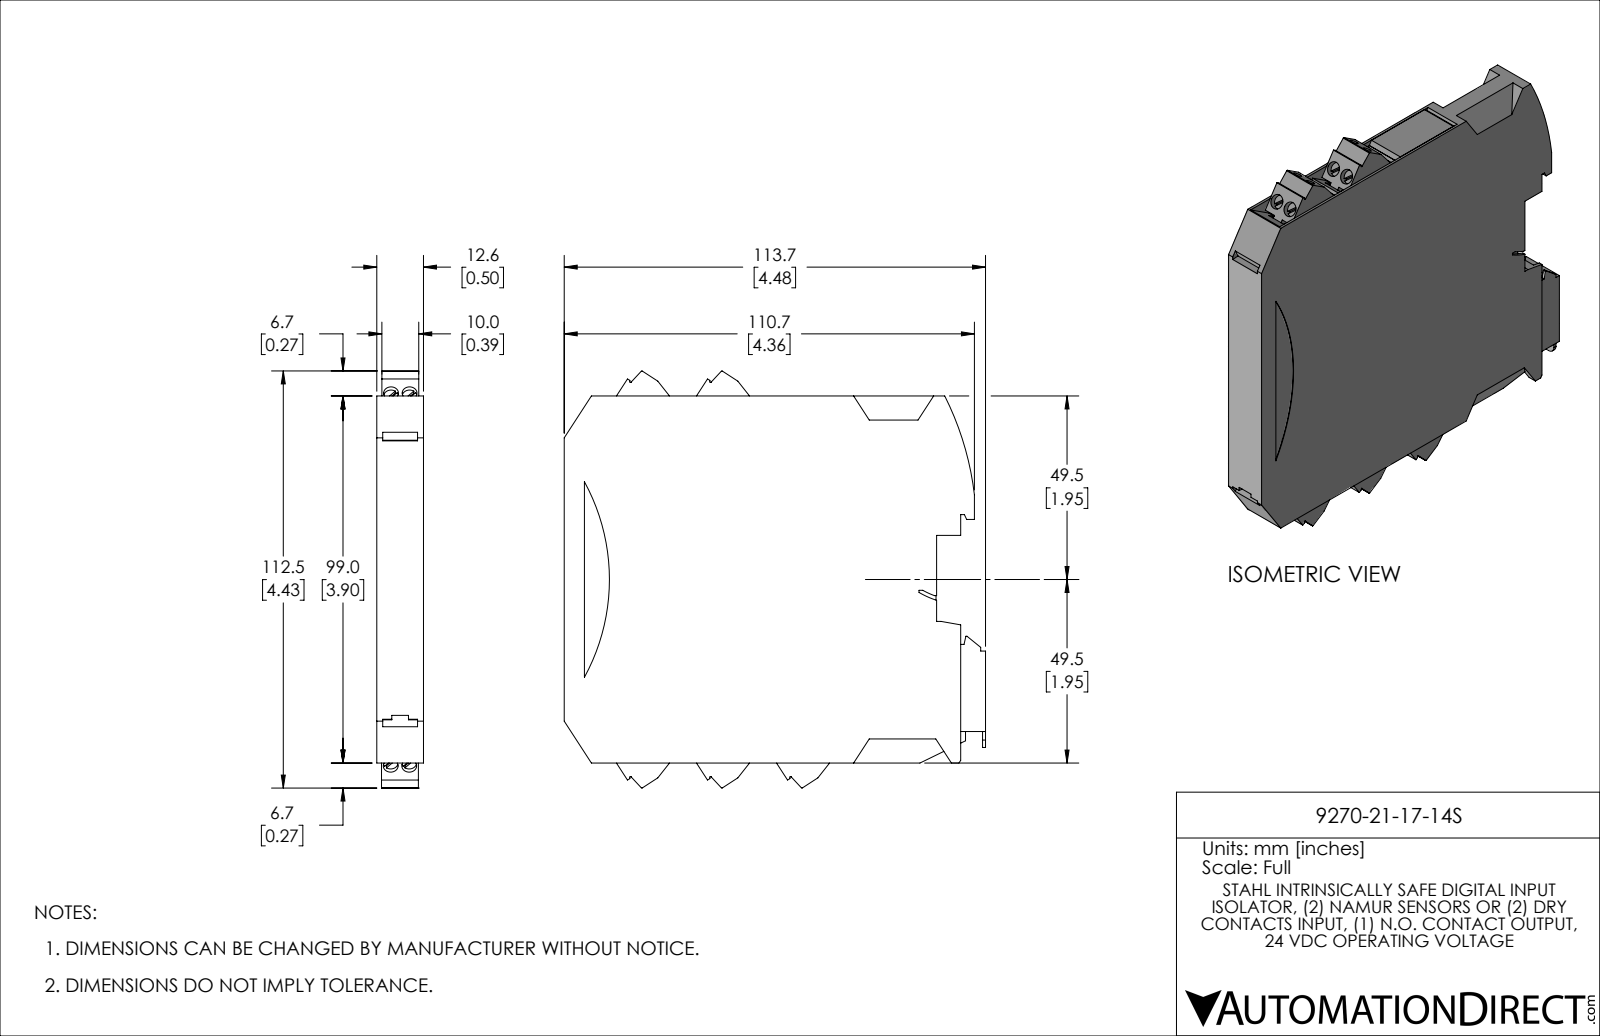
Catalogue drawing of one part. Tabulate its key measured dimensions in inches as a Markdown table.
| quantity | value |
| --- | --- |
| part name | 9270-21-17-14s |
| STEP written by | SolidWorks 2019 (AUTOMOTIVE_DESIGN) |
| units | inches |
| bodies | 7 solids, 956 faces (854 planar, 92 cylindrical, 10 other) |
| overall size | 4.476 × 4.429 × 0.496 |
| volume | 7.755 in³ |
| surface area | 64.57 in² |
| round holes (diameter × count) | 0.06 × 10, 0.088 × 10, 0.118 × 10, 0.157 × 10 |
| round bosses / shafts (diameter × count) | 0.11 × 6 |
| partial cylindrical surfaces (radius × count) | 0.118 × 13, 0.114 × 10, 0.055 × 6, 0.008 × 5, 0.079 × 2, 0.02 × 1, 0.059 × 1, 0.098 × 1 |
| main face-to-face distances | 0.496, 0.03, 0.467, 0.713, 0.392, 0.05, 0.446, 0.021, 0.416, 0.054 |
| hole center spacings | 0.197, 0.713, 0.74, 0.849, 0.872, 0.463, 0.503, 0.463 |
